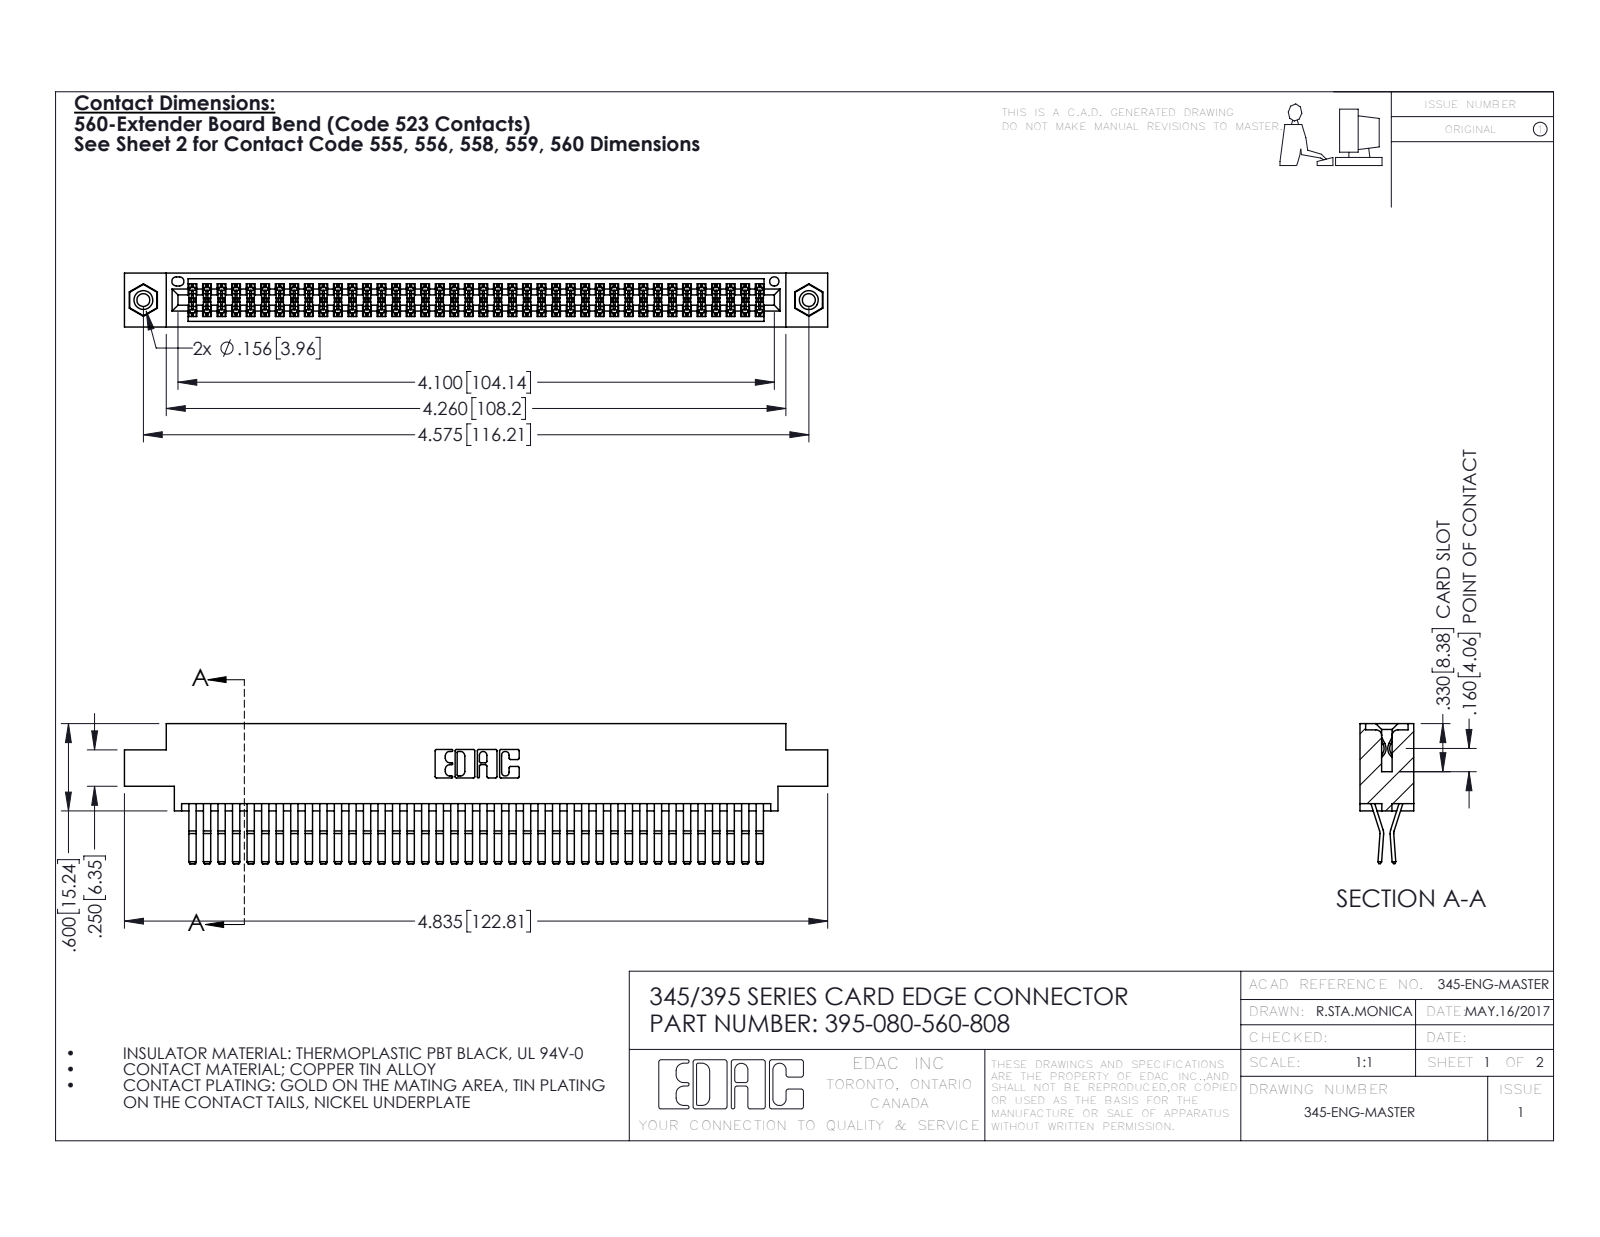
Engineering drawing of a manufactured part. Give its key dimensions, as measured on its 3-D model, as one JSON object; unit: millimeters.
{"part_name": "395-080-560-808; 345-250-001_345-250-003-102; 345-292-001_560 Tail; 345 Part_0.170 Offset - 0.156 Dia-TI", "step_written_by": "SolidWorks 2016 (CONFIG_CONTROL_DESIGN)", "units": "millimeters", "bodies": {"solids": 83, "faces": 4350, "planar": 2756, "cylindrical": 1578, "other": 16}, "overall_size": [122.8, 24.4, 9.4], "volume_mm3": 12300, "surface_area_mm2": 19670, "round_holes": [[2.3, 2], [3.2, 2], [4, 2], [1.6, 1]], "round_bosses_or_shafts": [[3.9, 2]], "partial_cylinders_radius": [[0.2, 120], [0.3, 22], [0.2, 6], [0.8, 6], [0.7, 3], [0.3, 2], [0.4, 2], [0.5, 2]], "face_to_face_distances": [0.6, 1.8, 7.6, 9.4, 5.1, 2.5, 6.9, 5.7, 4.4, 3.8], "hole_center_spacings": [6.9, 110.2, 116.2]}
